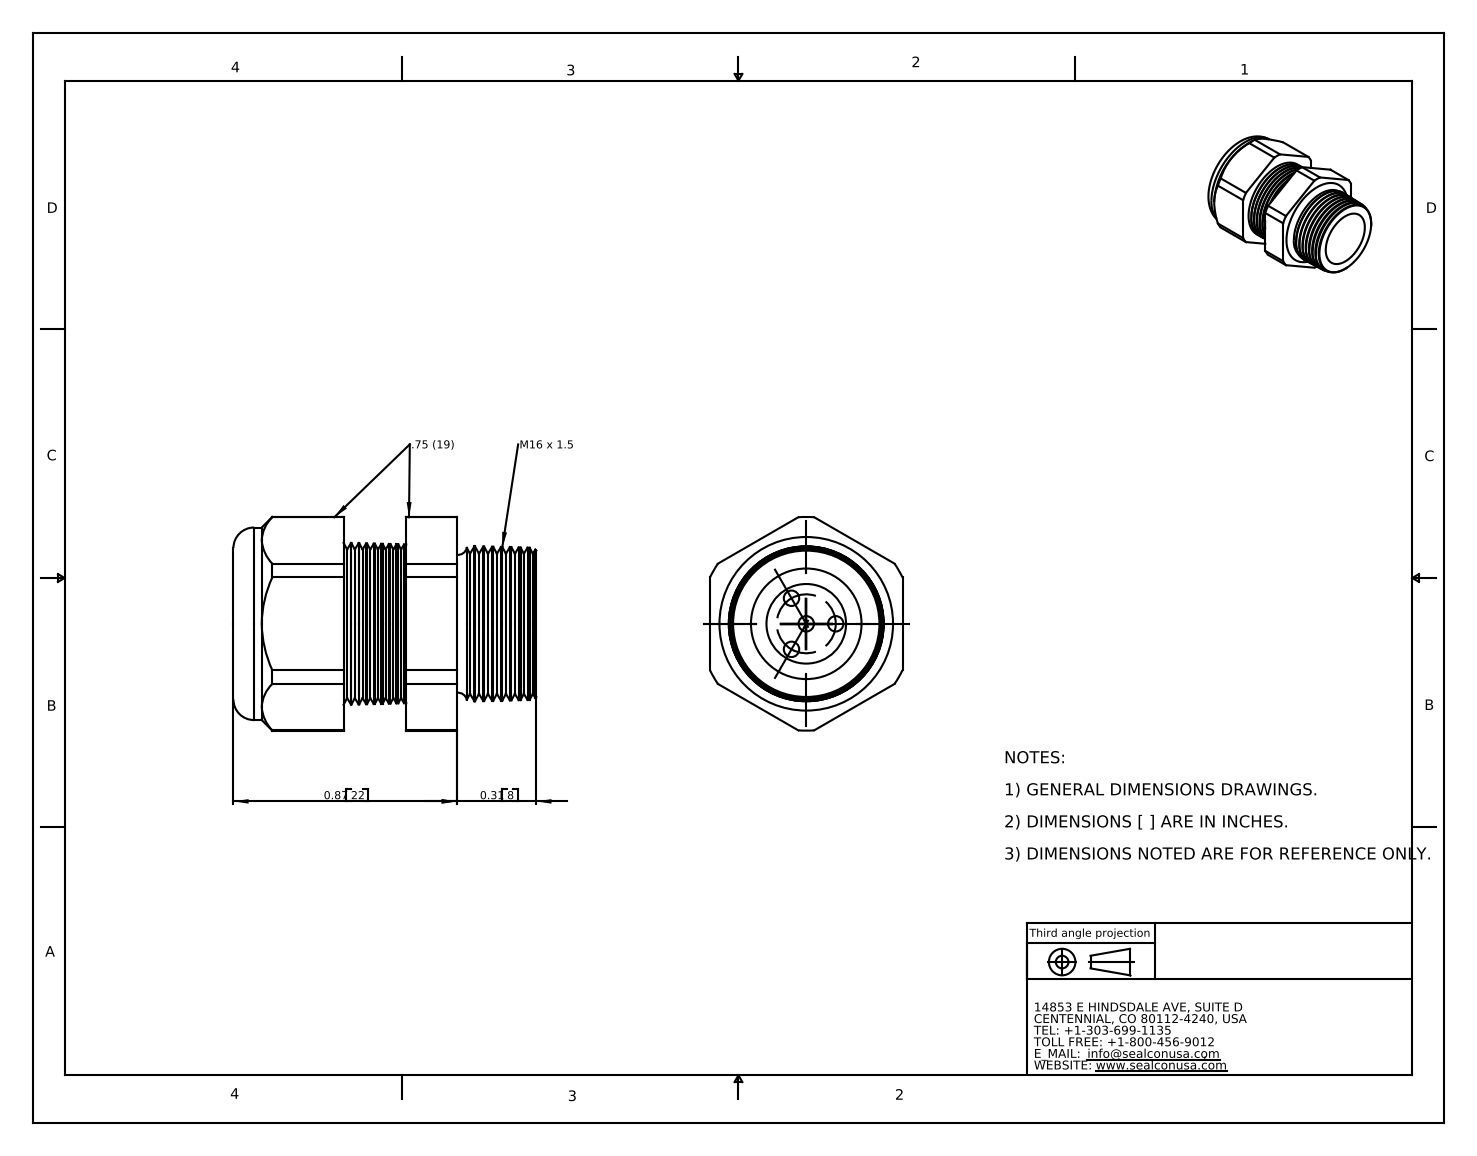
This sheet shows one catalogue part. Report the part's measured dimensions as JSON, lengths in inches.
{"part_name": "CD16M1-GY", "step_written_by": "SolidWorks 2007 (CONFIG_CONTROL_DESIGN)", "units": "inches", "bodies": {"solids": 2, "faces": 158, "planar": 20, "cylindrical": 28, "other": 110}, "overall_size": [1.18, 0.833, 0.75], "volume_in3": 0.336, "surface_area_in2": 6.185, "round_holes": [[0.06, 4], [0.29, 1], [0.31, 1]], "round_bosses_or_shafts": [[0.75, 1]], "partial_cylinders_radius": [[0.416, 1]], "face_to_face_distances": [0.75, 0.673, 0.75, 0.429, 0.244, 0.87, 0.441, 0.197, 1.18, 0.751], "hole_center_spacings": [0.115, 0.199]}
